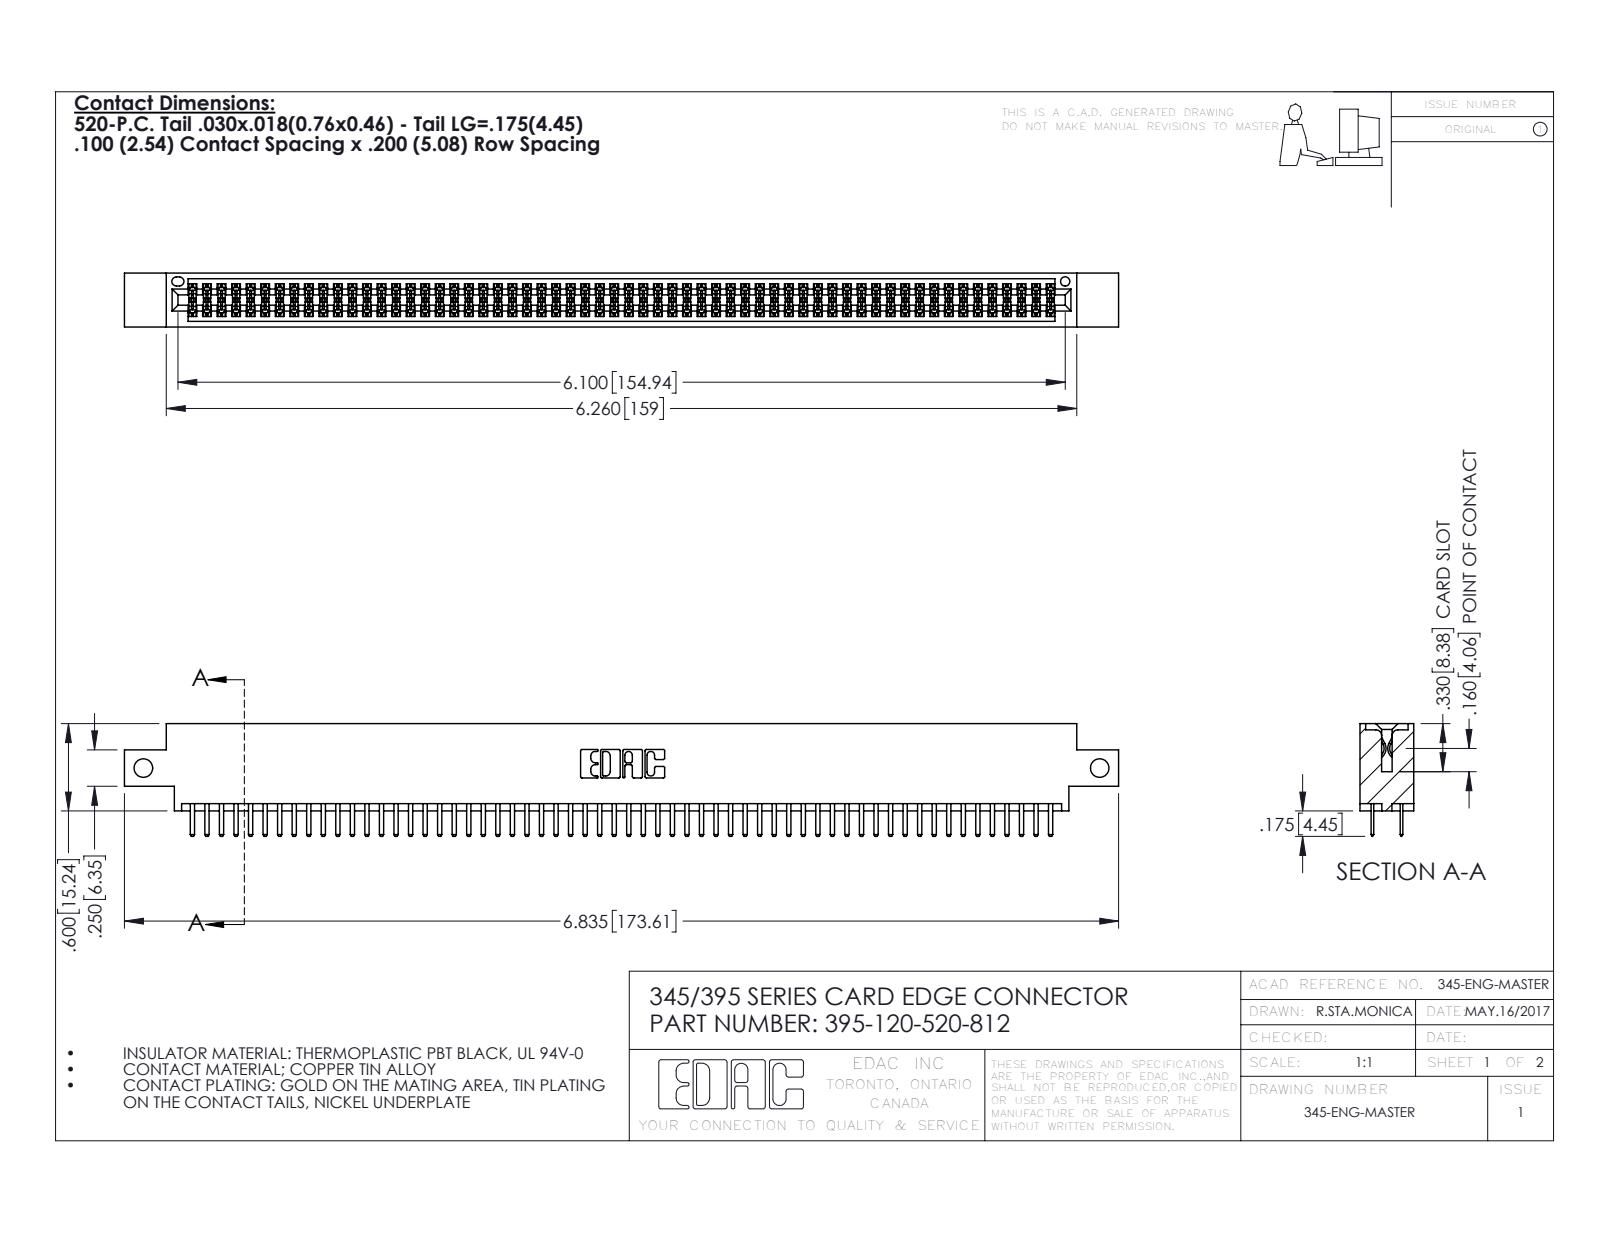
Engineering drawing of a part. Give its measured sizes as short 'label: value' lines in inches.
name: 345-292-001_345-293-120; 345 Part_0.170 Offset - Side Mount; 395-120-520-812
written by: SolidWorks 2016 (CONFIG_CONTROL_DESIGN)
unit: in
bodies: 121 solids, 6610 faces (4284 planar, 2326 cylindrical, 0 other)
size: 6.835 × 0.775 × 0.37
volume: 1.024 in³; area: 38.82 in²
holes: 2× ⌀0.128, 1× ⌀0.064
rounds: 180× R0.006, 124× R0.01, 22× R0.01, 6× R0.007, 6× R0.031, 3× R0.026, 2× R0.014, 2× R0.019
face distances: 0.298, 0.072, 0.2, 0.37, 0.098, 0.272, 0.025, 0.225, 0.022, 0.072
hole spacings: 6.575
